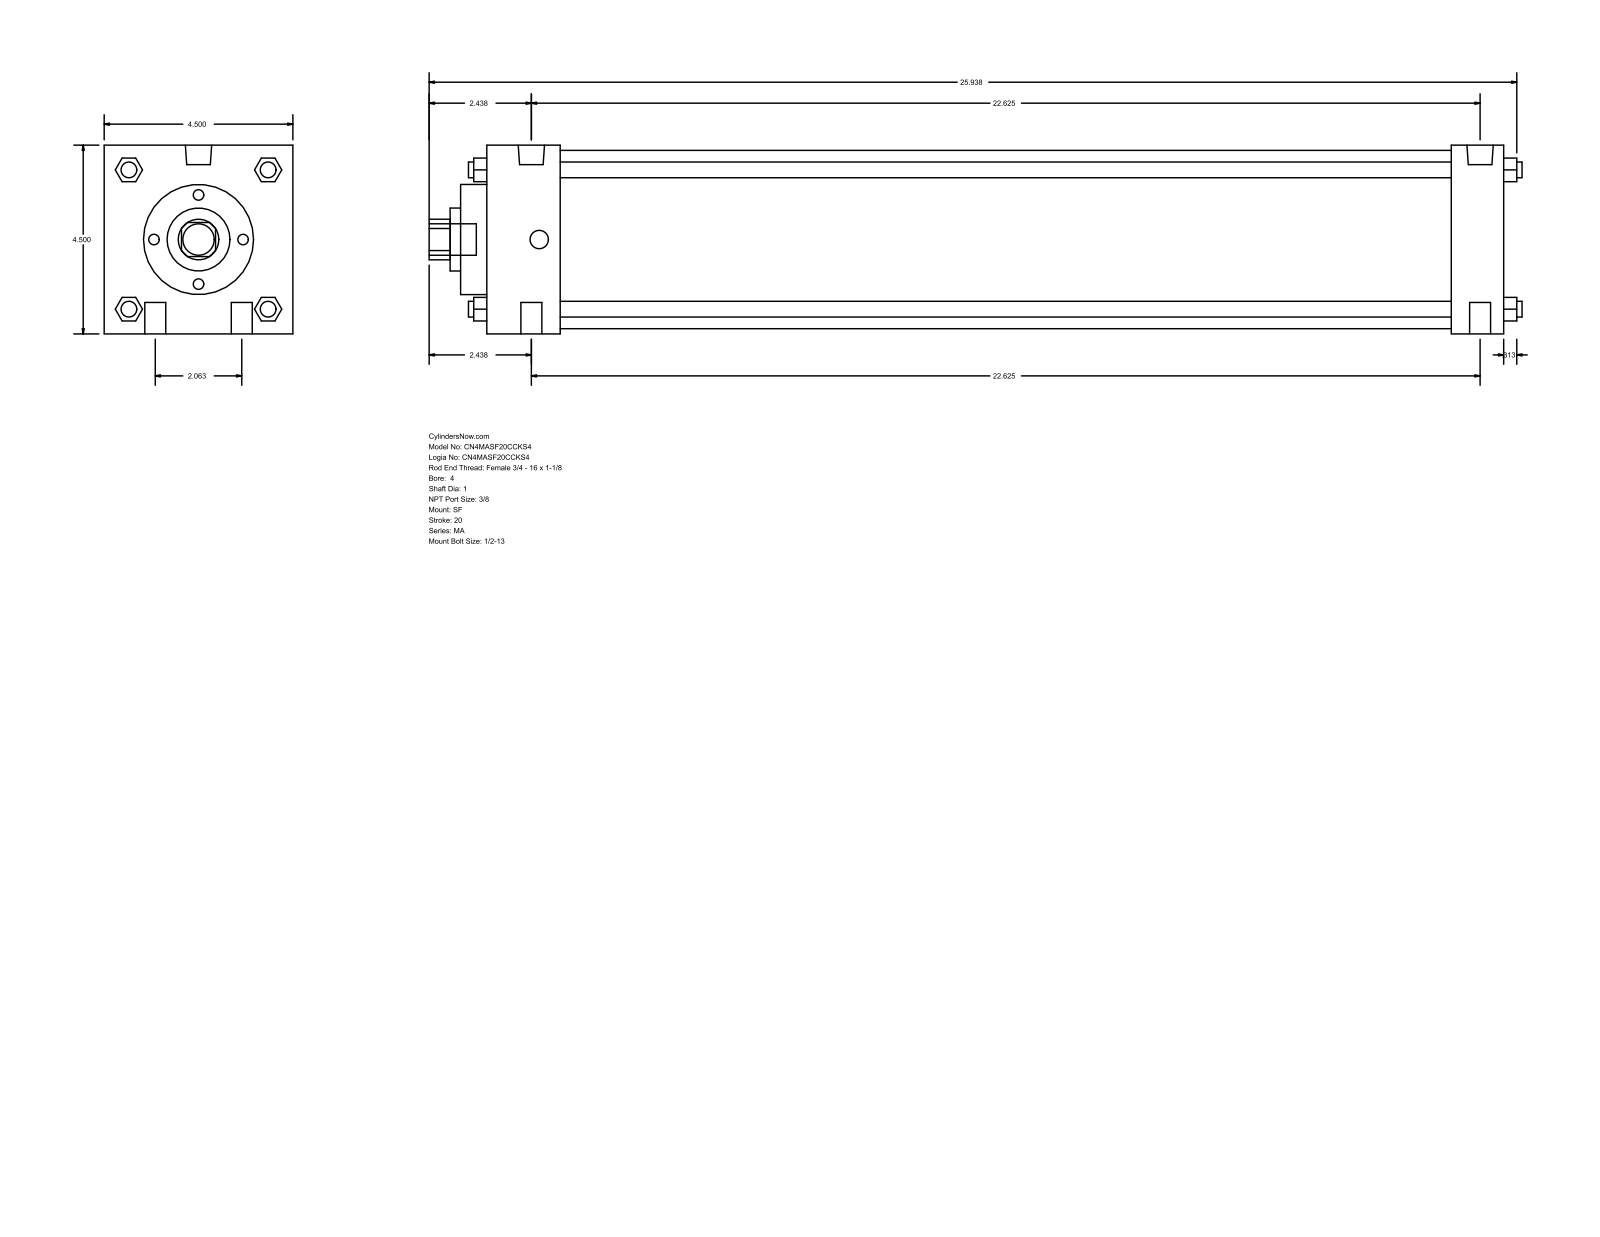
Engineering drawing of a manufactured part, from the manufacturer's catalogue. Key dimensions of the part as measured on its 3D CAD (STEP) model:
Part name (STEP PRODUCT): MA_SF__0400_1
STEP written by: GSSL Pune (CONFIG_CONTROL_DESIGN)
Units: millimetres
Bodies: 0 solids, 126 faces (95 planar, 31 cylindrical, 0 other)
Overall size (bounding box): 661.99 × 114.3 × 114.3
Round holes (diameter × count): ⌀25.4 ×1, ⌀38.1 ×1, ⌀66.67 ×1, ⌀107.95 ×1
Round bosses / shafts (diameter × count): ⌀12.7 ×4, ⌀9.53 ×4, ⌀15.93 ×2, ⌀11.11 ×2, ⌀19.05 ×1
Partial cylindrical surfaces — rounded edges, fillets, slot ends (radius × count): R12.29 ×1
Main face-to-face distances: 114.3, 615.96, 584.2, 31.76, 44.46, 539.74, 571.5, 15.87, 60.33, 600.07
